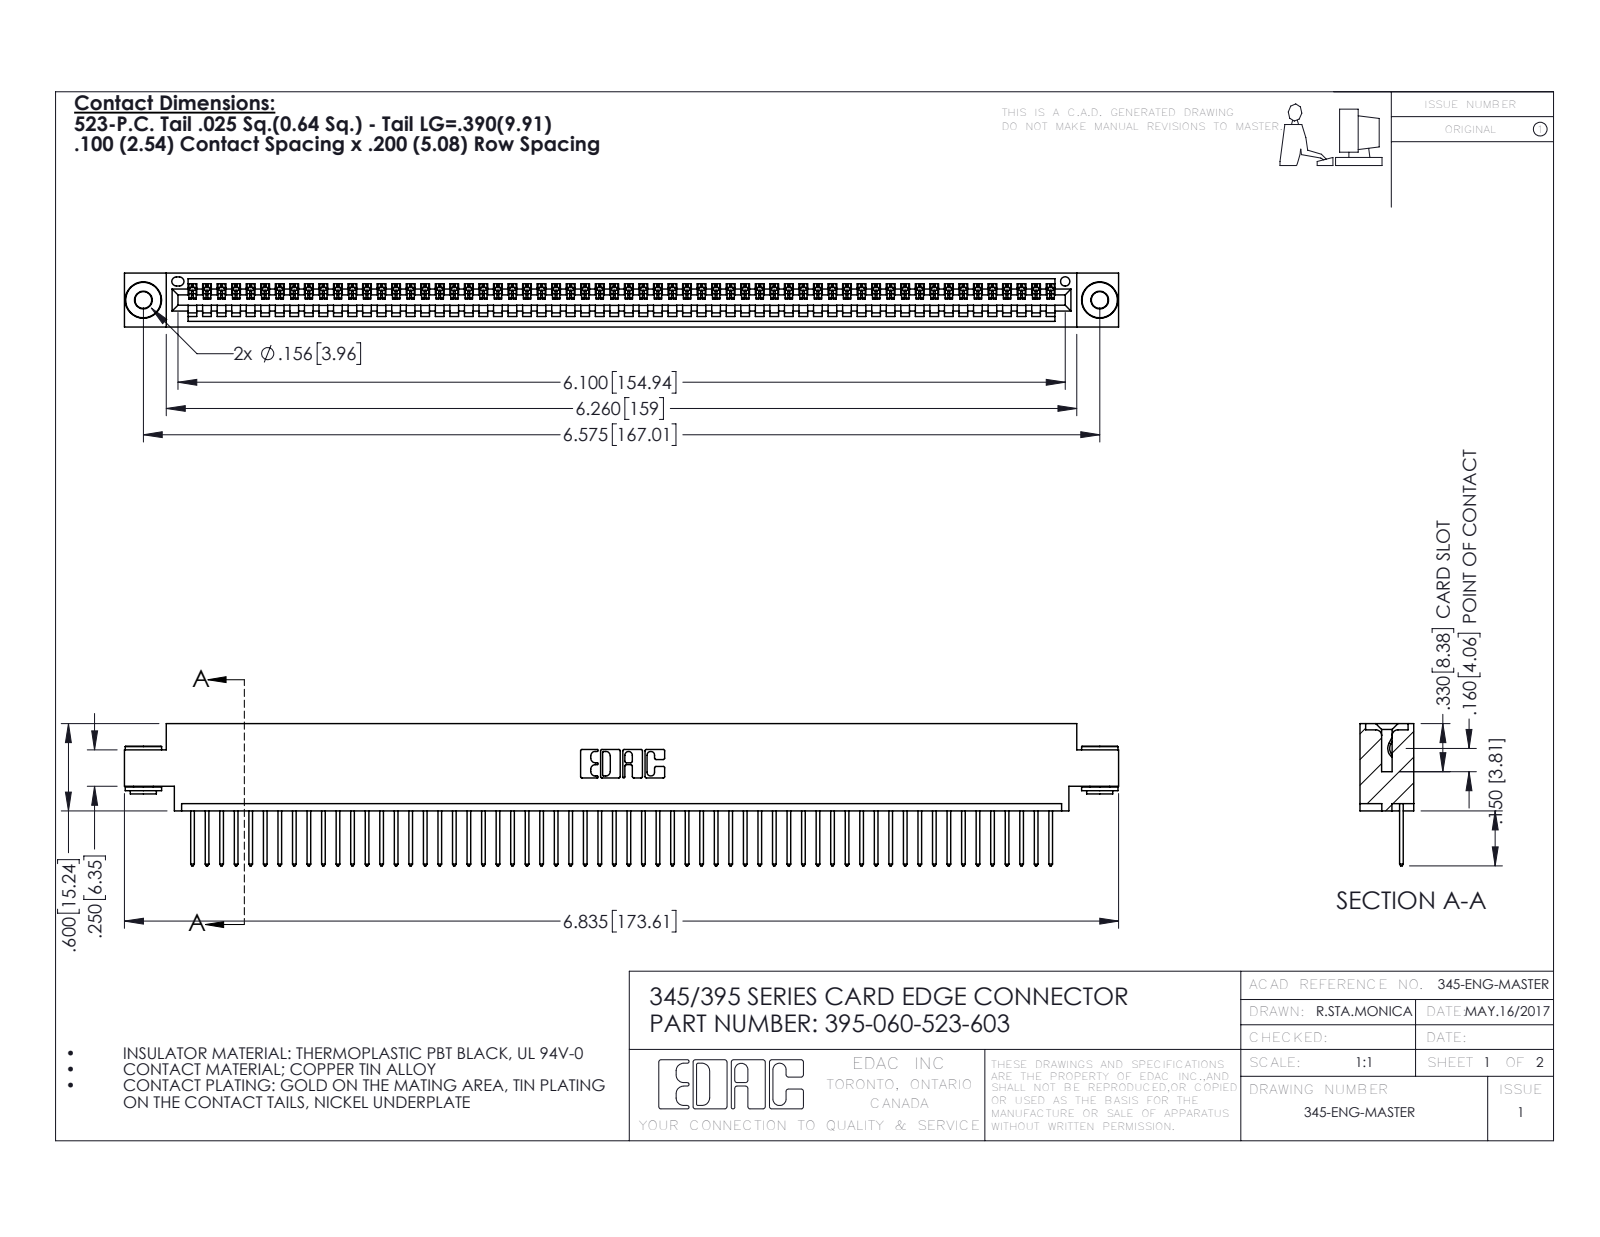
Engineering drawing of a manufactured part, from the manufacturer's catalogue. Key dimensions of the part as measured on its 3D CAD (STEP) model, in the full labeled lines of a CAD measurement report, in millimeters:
Part name (STEP PRODUCT): 345-250-002_345-250-002-102; 395-060-523-603; 345-292-001_345-293-123; 345 Part_0.170 Offset - 0.156 Dia-TH
STEP written by: SolidWorks 2016 (CONFIG_CONTROL_DESIGN)
Units: millimetres
Bodies: 63 solids, 3648 faces (2494 planar, 1146 cylindrical, 8 other)
Overall size (bounding box): 173.6 × 24.8 × 9.4
Volume: 16 520 mm³ · Surface area: 22 610 mm²
Round holes (diameter × count): ⌀2.9 ×2, ⌀4 ×2, ⌀1.6 ×1
Round bosses / shafts (diameter × count): ⌀6.4 ×2, ⌀4.6 ×2, ⌀3.5 ×2
Partial cylindrical surfaces — rounded edges, fillets, slot ends (radius × count): R0.2 ×120, R0.3 ×120, R0.3 ×22, R0.2 ×6, R0.8 ×6, R0.7 ×3, R0.8 ×2, R1 ×2
Main face-to-face distances: 1.8, 7.6, 9.4, 2.5, 6.9, 0.6, 5.1, 5.7, 4.4, 3.8
Hole centre spacings: 6.9, 161, 167
